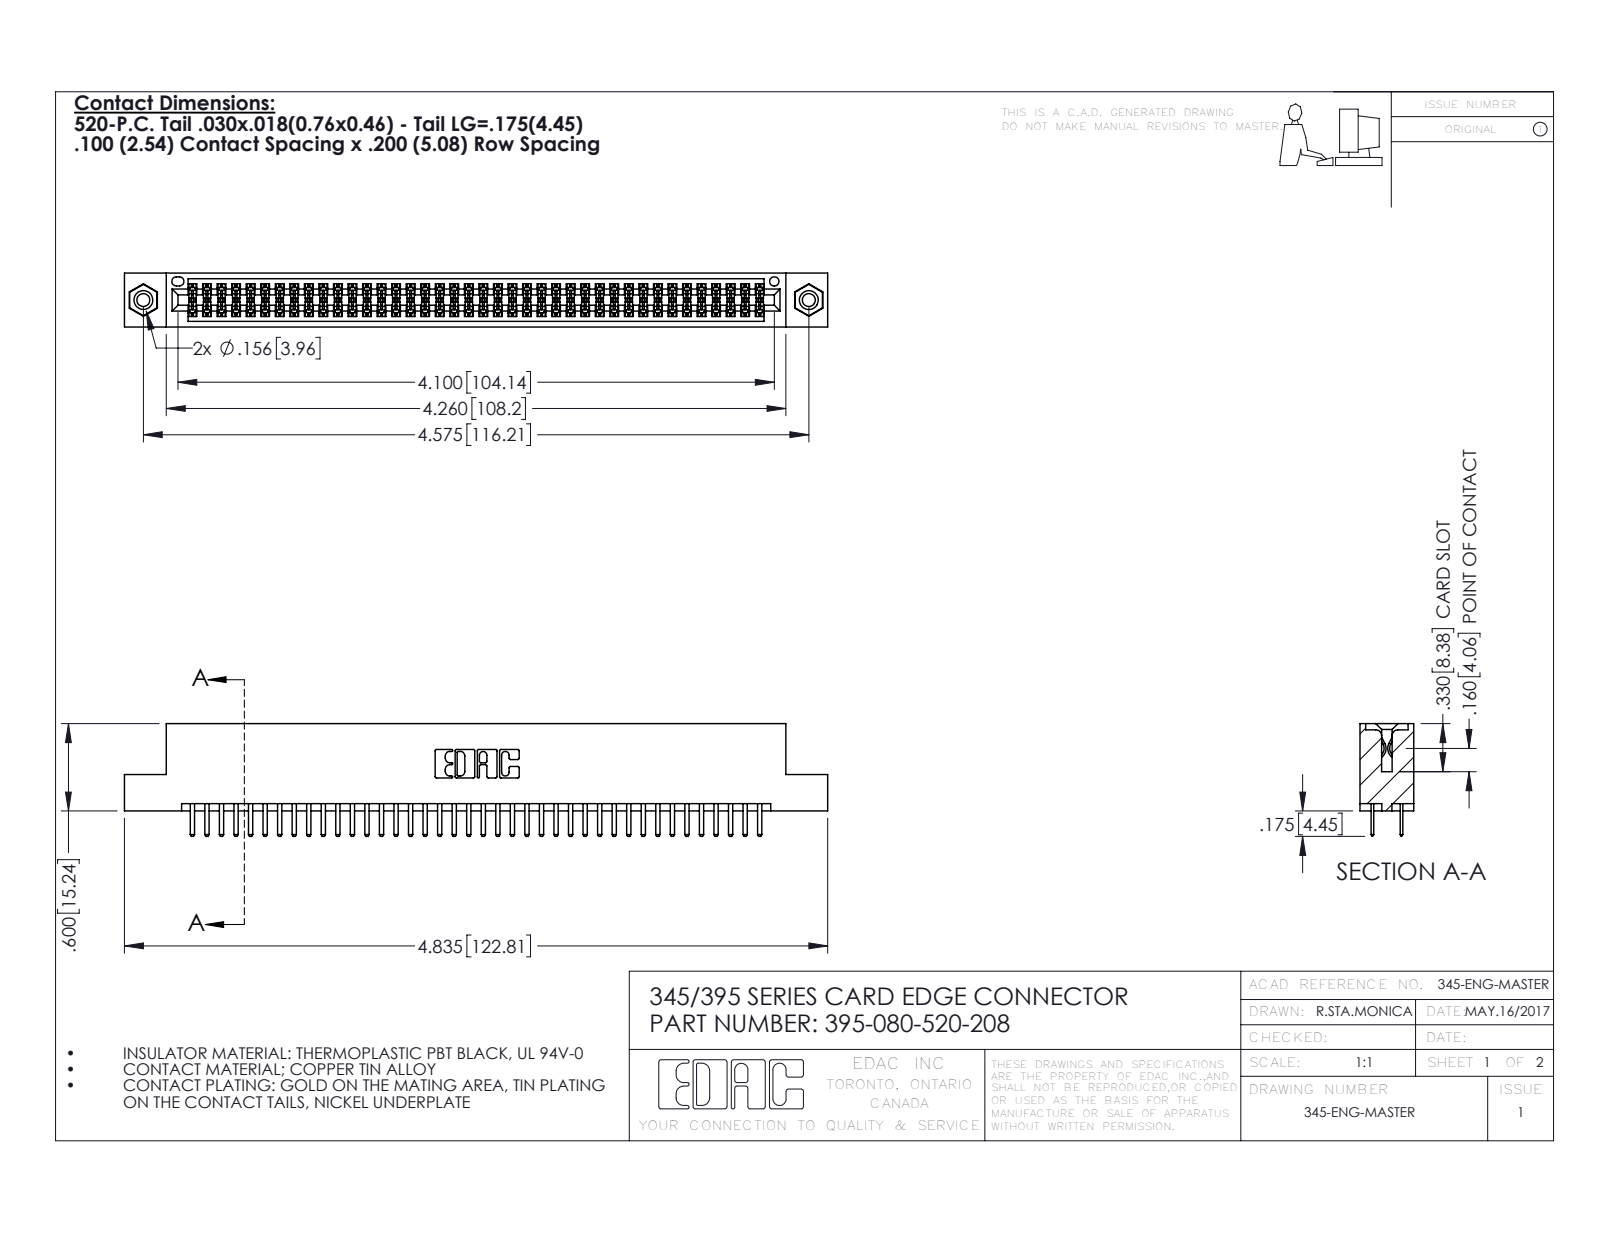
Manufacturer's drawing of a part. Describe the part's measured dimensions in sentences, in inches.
The part is named "345 Part_Flush Mounting Lugs - 0.156 Dia-TI; 345-250-001_345-250-003-102; 345-292-001_345-293-120; 395-080-520-208". Its 3-D file was written by "SolidWorks 2016 (CONFIG_CONTROL_DESIGN)". It is 83 solids with 4506 faces: 2912 planar, 1578 cylindrical and 16 other. Overall it measures 4.835 by 0.775 by 0.37 inches. Its volume is 0.724 cubic inches and its surface area 27.04 square inches. Round holes: 2 of diameter 0.089, 2 of diameter 0.125, 2 of diameter 0.156, 1 of diameter 0.064. Round bosses or shafts: 2 of diameter 0.155. Partial cylindrical surfaces (rounded edges, fillets, slot ends): 120 of radius 0.006, 84 of radius 0.01, 22 of radius 0.01, 6 of radius 0.007, 6 of radius 0.031, 3 of radius 0.026, 2 of radius 0.014, 2 of radius 0.019. The main face-to-face distances are 0.072, 0.298, 0.2, 0.37, 0.098, 0.272, 0.025, 0.225, 0.022, 0.072. The hole center spacings are 0.27, 4.339, 4.575.
